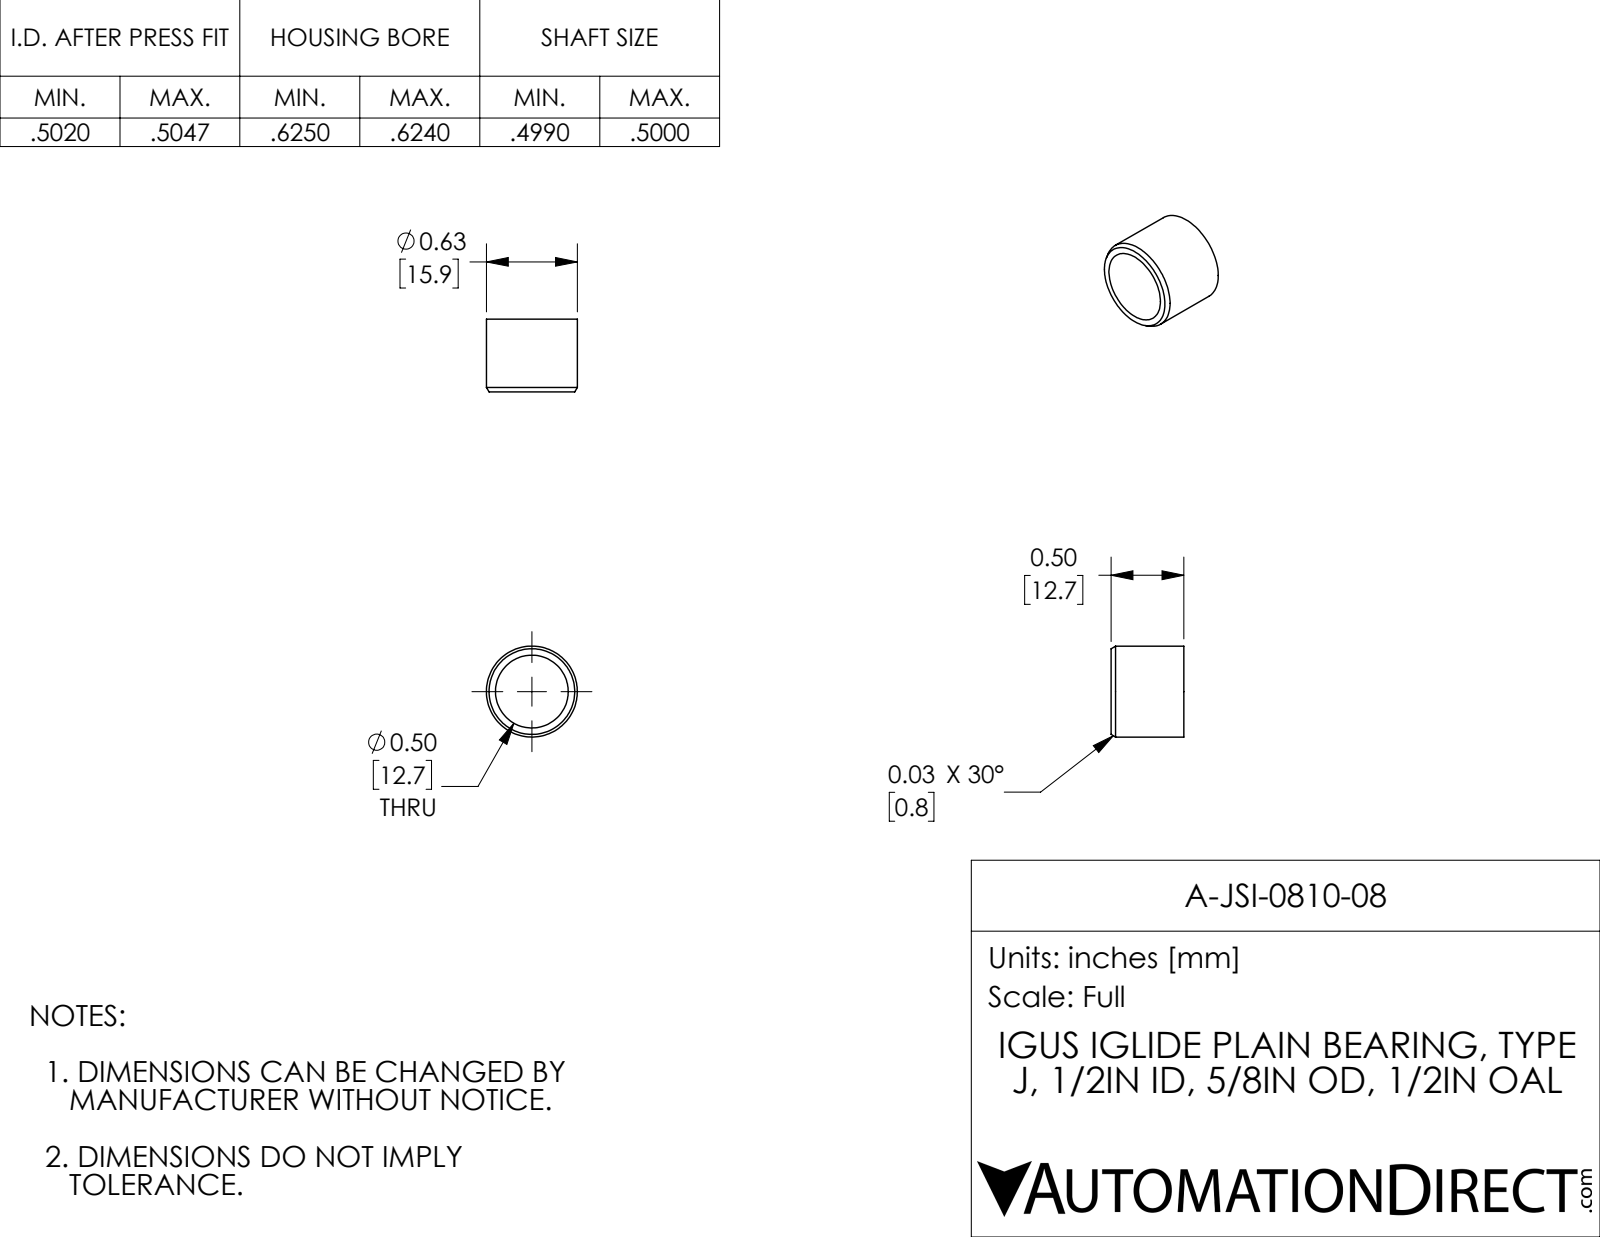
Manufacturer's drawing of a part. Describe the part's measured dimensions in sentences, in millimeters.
The part is named "A-JSI-0810-08". Its 3-D file was written by "SolidWorks 2017 (AUTOMOTIVE_DESIGN)". It is 1 solid with 10 faces: 2 planar, 4 cylindrical and 4 other. Overall it measures 15.9 by 15.9 by 12.7 millimeters. Its volume is 880 cubic millimeters and its surface area 1 257 square millimeters. Round holes: 1 of diameter 12.7. Round bosses or shafts: 1 of diameter 15.9. The main face-to-face distances are 12.7.
